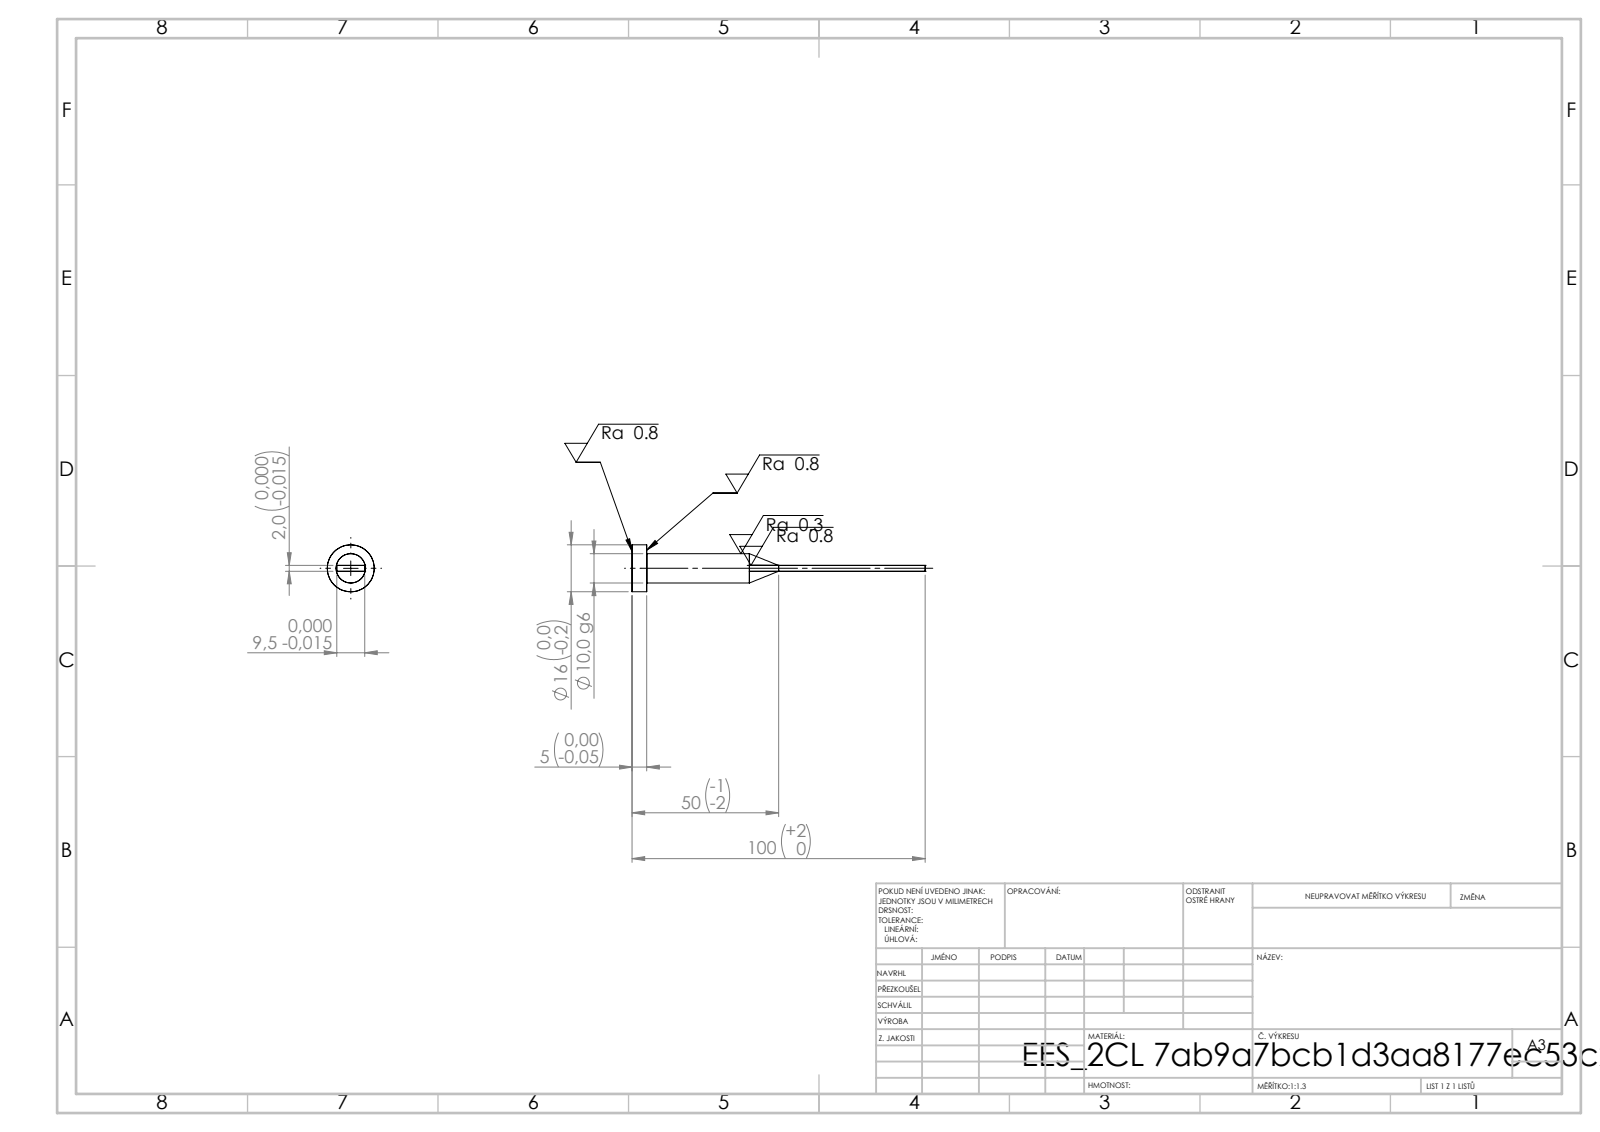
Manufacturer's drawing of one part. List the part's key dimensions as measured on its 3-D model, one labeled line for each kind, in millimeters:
STEP written by: SolidWorks 2019 (CONFIG_CONTROL_DESIGN)
Units: millimetres
Bodies: 1 solid, 15 faces (7 planar, 4 cylindrical, 4 other)
Overall size (bounding box): 100 × 16 × 16
Volume: 5 170 mm³ · Surface area: 3 113 mm²
Round bosses / shafts (diameter × count): ⌀16 ×1, ⌀10 ×1
Main face-to-face distances: 2, 5, 9.5, 100, 95
